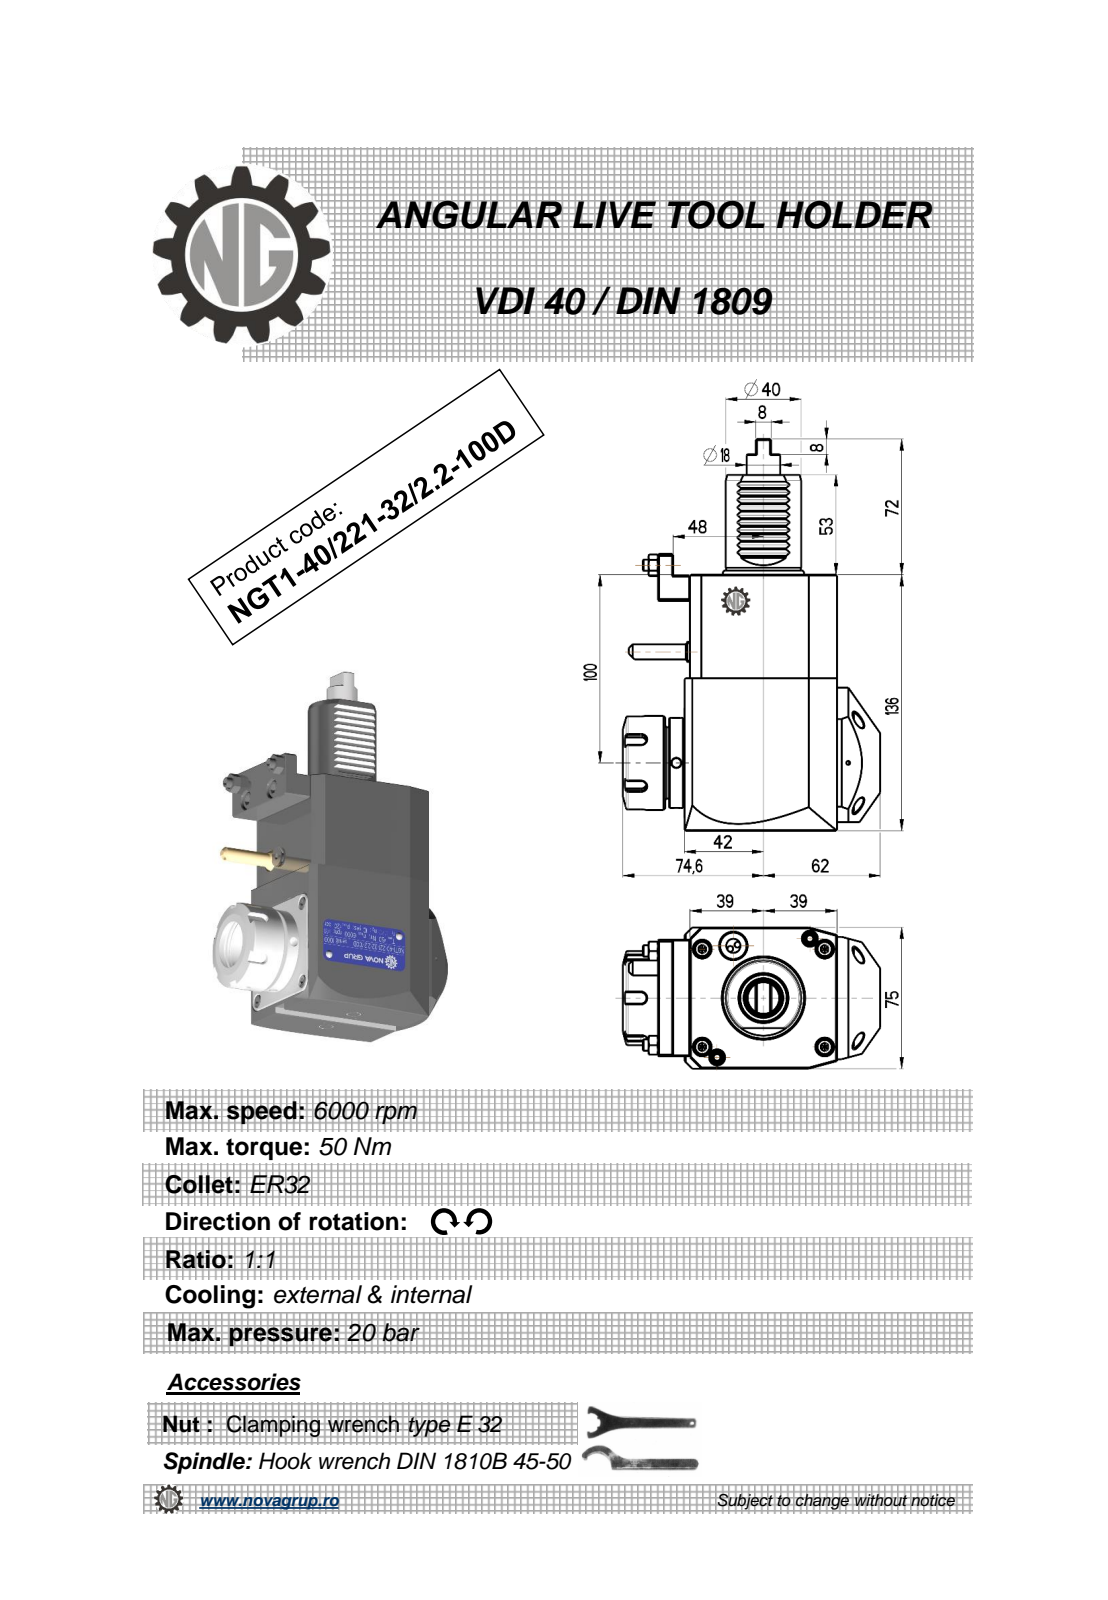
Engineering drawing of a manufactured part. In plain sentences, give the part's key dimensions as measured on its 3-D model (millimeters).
The part is named "NGT1_40_221_32_2_2_100D". Its 3-D file was written by "PRO/ENGINEER BY PARAMETRIC TECHNOLOGY CORPORATION, 2010280 (CONFIG_CONTROL_DESIGN)". It is 1 solid with 383 faces: 173 planar, 77 cylindrical and 133 other. Overall it measures 208 by 136.6 by 76.6 millimeters. Its volume is 1 009 000 cubic millimeters and its surface area 77 217 square millimeters. Round holes: 3 of diameter 5, 1 of diameter 3, 1 of diameter 27. Round bosses or shafts: 2 of diameter 6, 1 of diameter 50, 1 of diameter 48, 1 of diameter 41, 1 of diameter 40, 1 of diameter 17.8, 1 of diameter 11.2, 1 of diameter 8. Partial cylindrical surfaces (rounded edges, fillets, slot ends): 10 of radius 0.3, 10 of radius 0.31, 6 of radius 0.22, 5 of radius 3, 2 of radius 0.8, 1 of radius 0.5, 1 of radius 40. The main face-to-face distances are 75, 136, 78, 14, 81, 3, 2.8, 80.8, 0.5, 118. The hole center spacings are 61.13.
